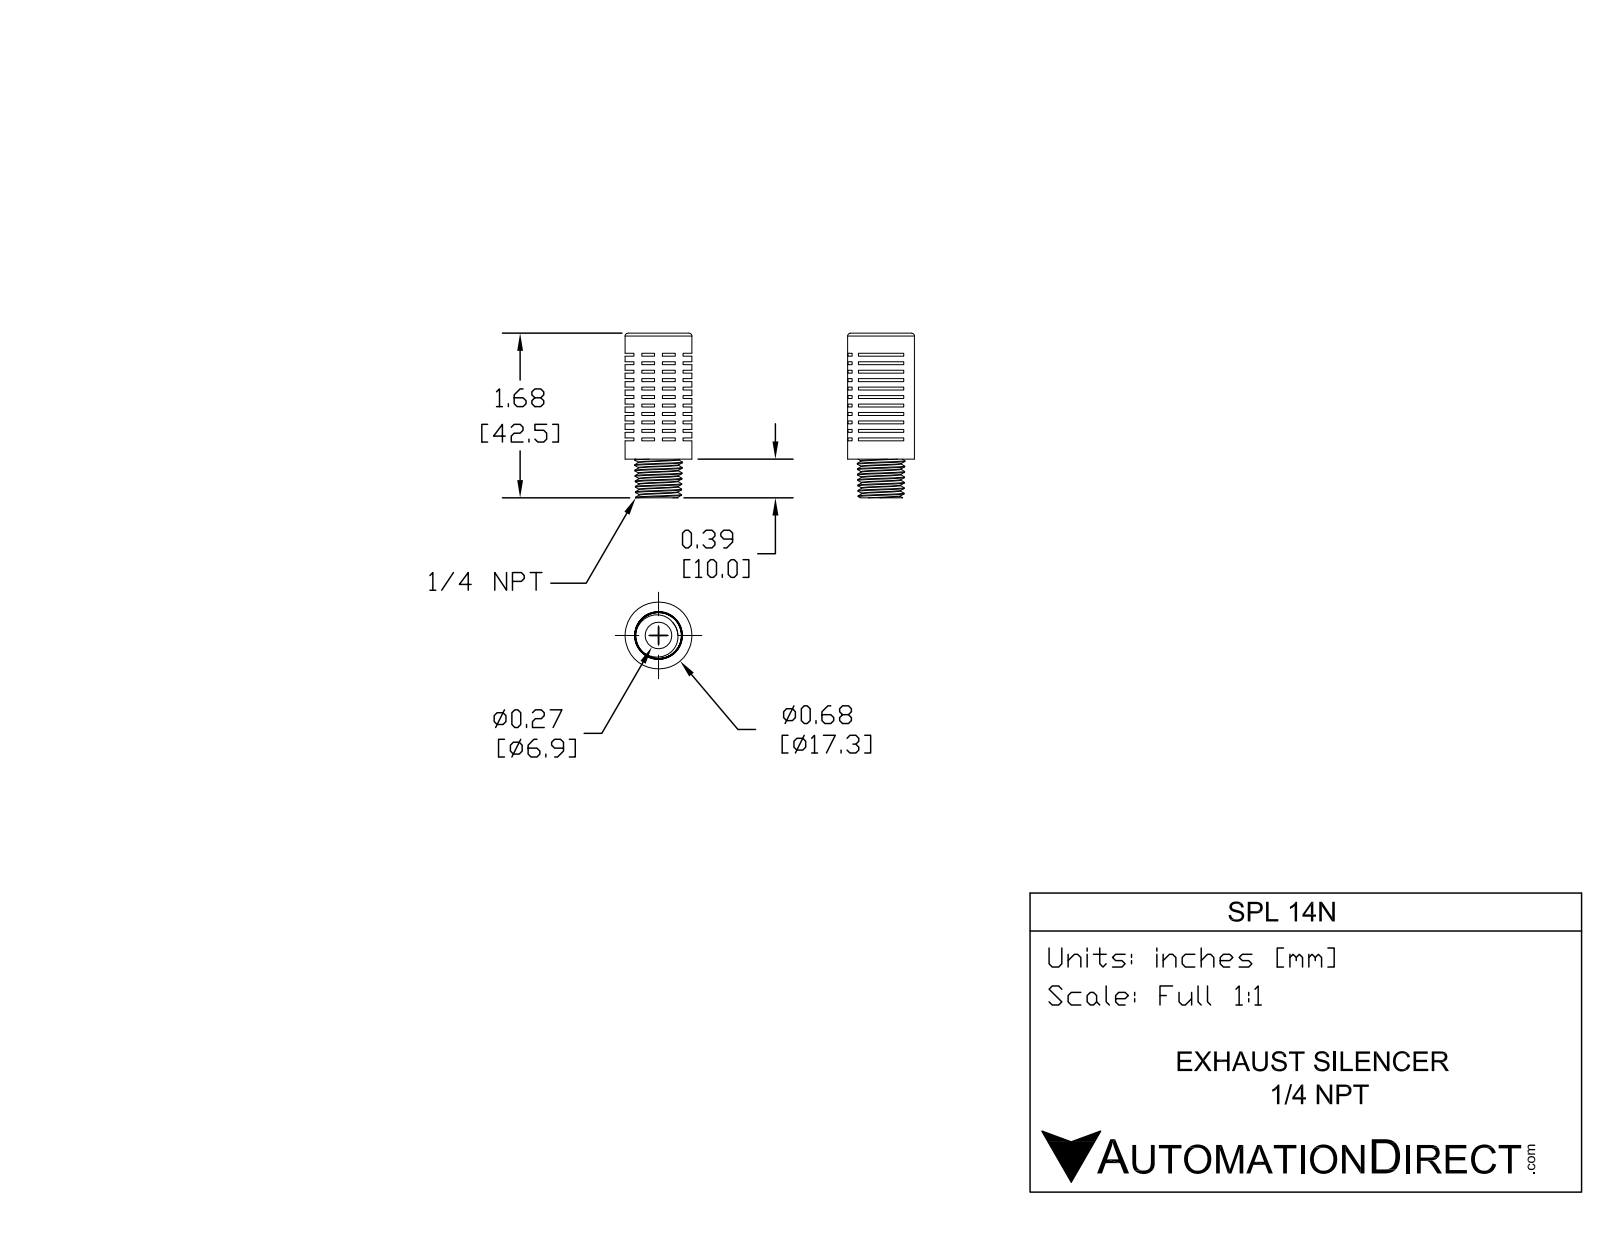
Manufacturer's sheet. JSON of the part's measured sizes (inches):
{"part_name": "SPL-14N", "step_written_by": "SolidWorks 2015 (CONFIG_CONTROL_DESIGN)", "units": "inches", "bodies": {"solids": 1, "faces": 228, "planar": 203, "cylindrical": 4, "other": 21}, "overall_size": [1.675, 0.68, 0.68], "volume_in3": 0.381, "surface_area_in2": 9.897, "round_holes": [[0.27, 1]], "round_bosses_or_shafts": [[0.68, 1]], "face_to_face_distances": [0.172, 0.086, 0.258, 0.43, 0.03, 0.056, 0.344, 0.202, 0.228, 0.086]}
